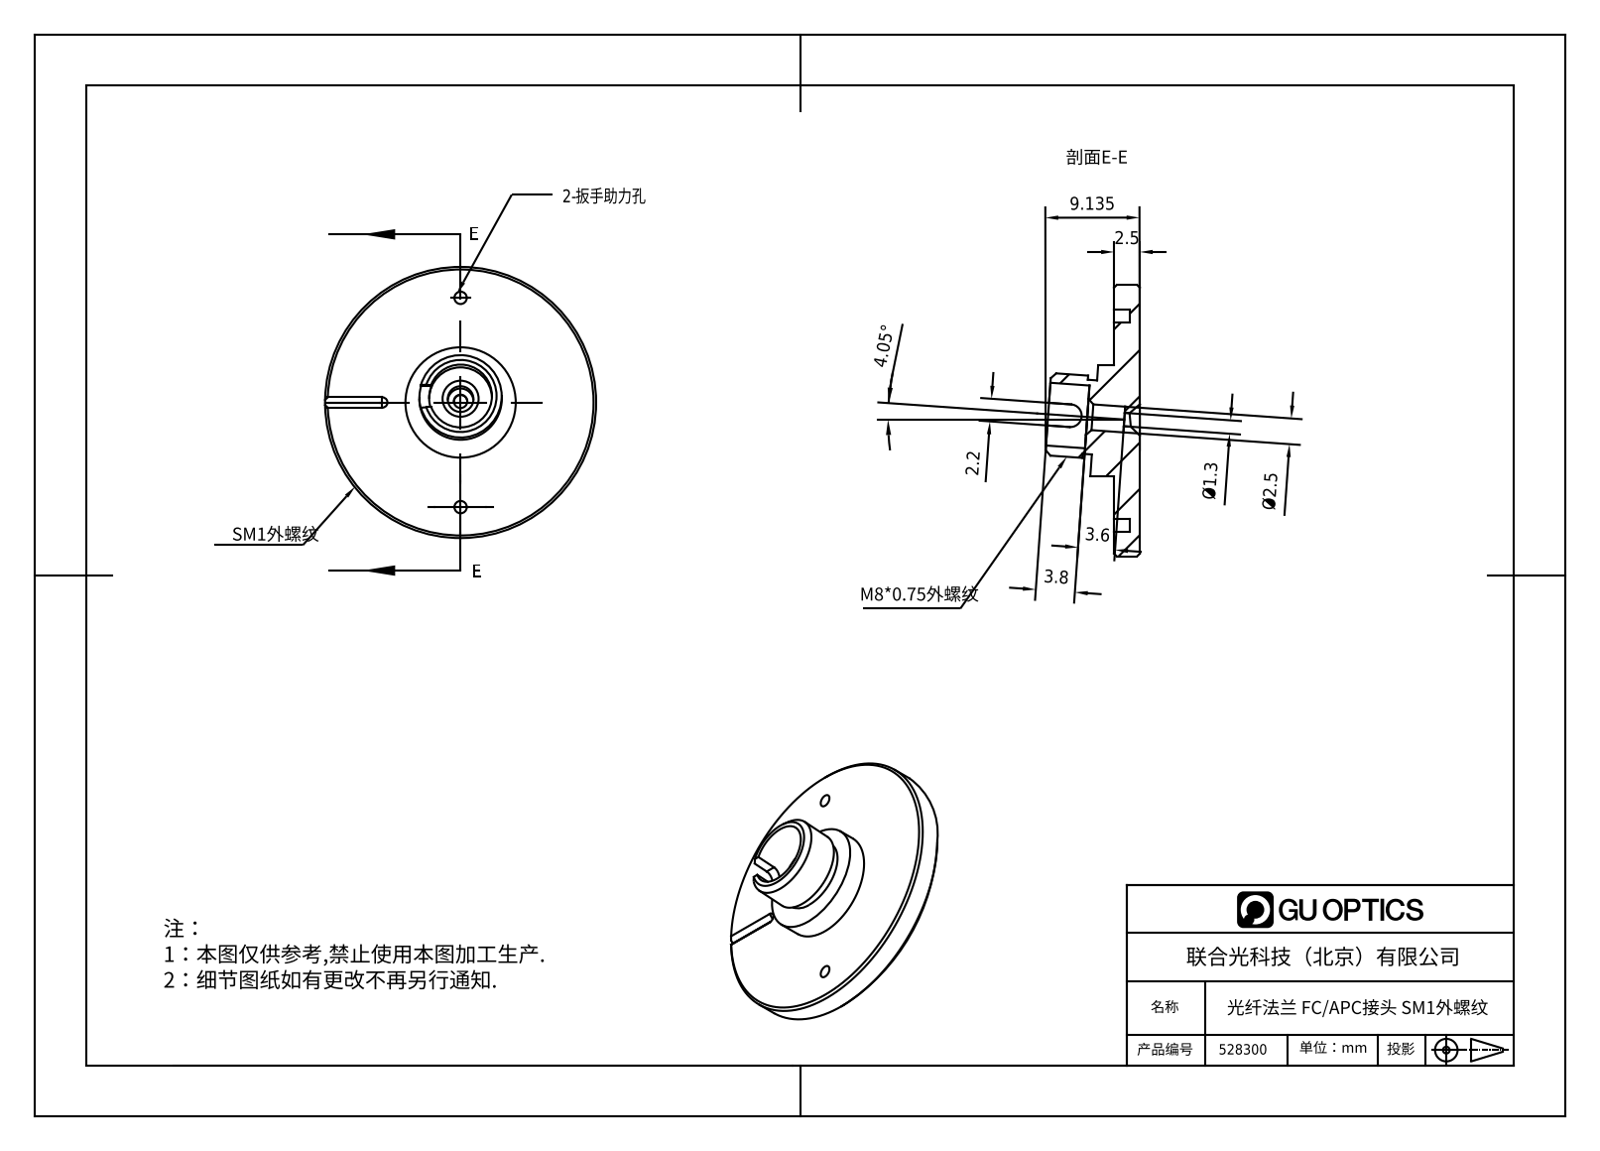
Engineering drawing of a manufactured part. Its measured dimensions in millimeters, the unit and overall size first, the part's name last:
Units: millimetres
Overall size (bounding box): 26.3 × 26.3 × 9.13
Round holes (diameter × count): ⌀1.2 ×2, ⌀1.3 ×1, ⌀2.5 ×1, ⌀6.1 ×1
Round bosses / shafts (diameter × count): ⌀26.3 ×1, ⌀10.7 ×1, ⌀8 ×1, ⌀7.2 ×1
Partial cylindrical surfaces — rounded edges, fillets, slot ends (radius × count): R1.1 ×1
Main face-to-face distances: 2.5, 0.7, 0.9, 4.51, 3.81, 3.61, 2.9, 3.6, 3.8, 7.41
Hole centre spacings: 20.3
Volume: 1 595 mm³ · Surface area: 1 563 mm²
Bodies: 1 solid, 47 faces (14 planar, 20 cylindrical, 13 other)
Part name (STEP PRODUCT): 528300，光纤法兰 FC-APC接头 SM1外螺纹
STEP written by: SolidWorks 2020 (CONFIG_CONTROL_DESIGN)
